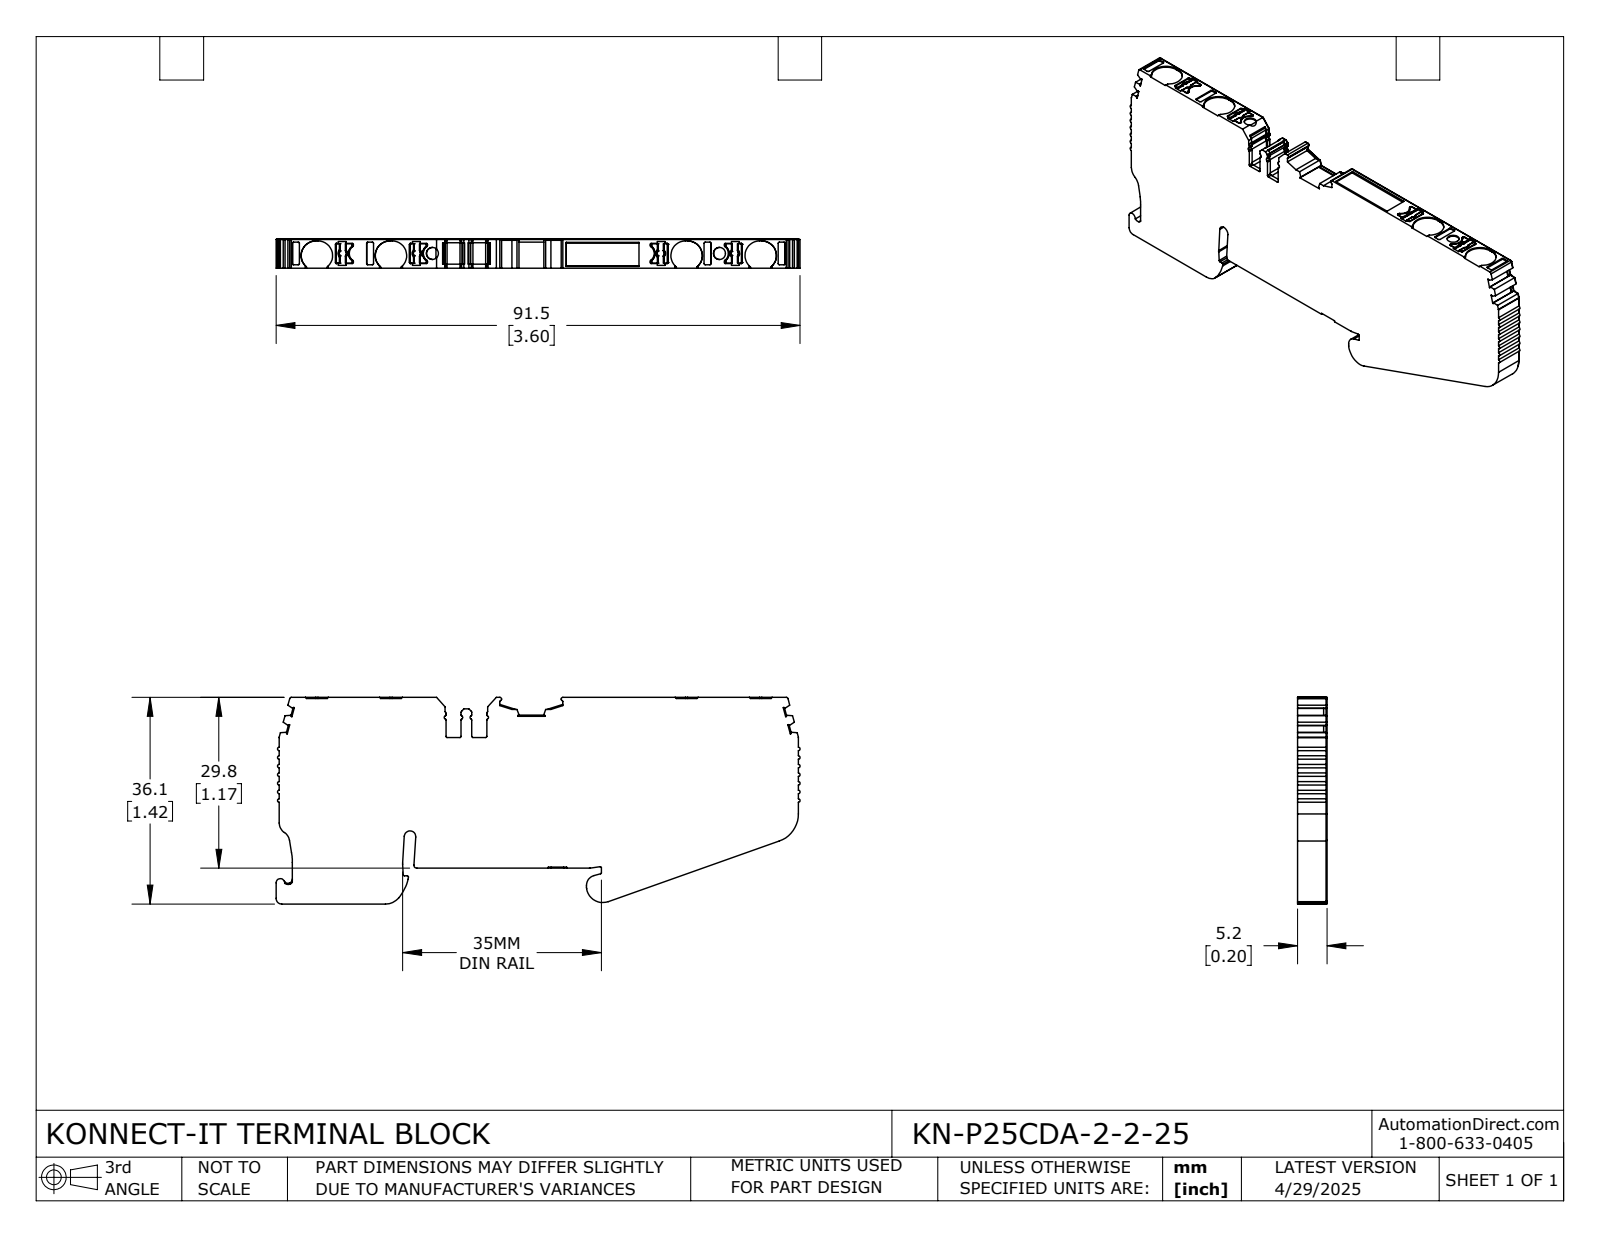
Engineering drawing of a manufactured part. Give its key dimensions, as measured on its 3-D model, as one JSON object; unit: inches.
{"part_name": "KN-P25CDA-2-2-25", "step_written_by": "SolidWorks 2024 (CONFIG_CONTROL_DESIGN)", "units": "inches", "bodies": {"solids": 1, "faces": 748, "planar": 386, "cylindrical": 291, "other": 71}, "overall_size": [3.602, 1.42, 0.203], "volume_in3": 0.855, "surface_area_in2": 11.07, "round_holes": [[0.083, 2]], "partial_cylinders_radius": [[0.008, 78], [0.012, 39], [0.004, 21], [0.02, 18], [0.006, 16], [0.016, 9], [0.1, 8], [0.059, 4]], "face_to_face_distances": [0.203, 1.166, 1.174, 0.246, 1.412, 1.42, 3.569, 0.197, 0.177, 0.047], "hole_center_spacings": [1.973]}
